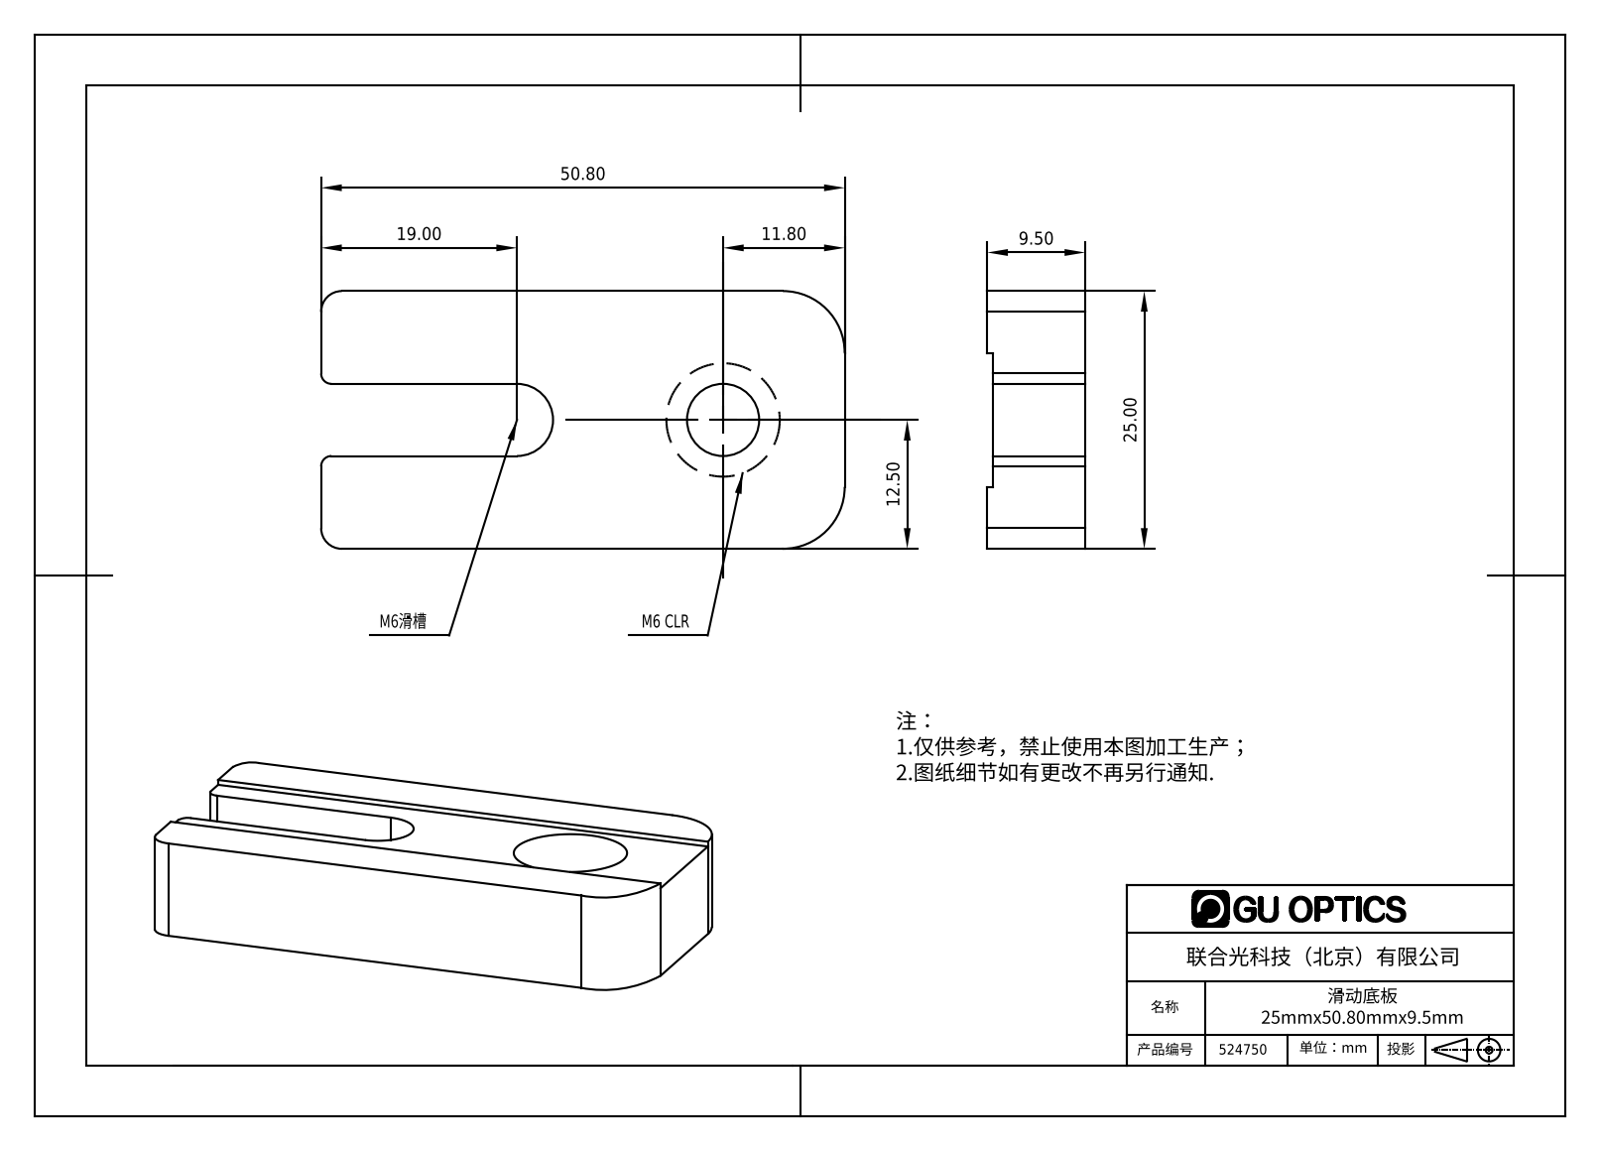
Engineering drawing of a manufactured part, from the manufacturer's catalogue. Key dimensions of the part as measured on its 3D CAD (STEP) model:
Part name (STEP PRODUCT): SB-05
STEP written by: SolidWorks 2012 (CONFIG_CONTROL_DESIGN)
Units: millimetres
Bodies: 1 solid, 23 faces (14 planar, 9 cylindrical, 0 other)
Overall size (bounding box): 50.8 × 25 × 9.5
Volume: 9 512 mm³ · Surface area: 4 180 mm²
Round holes (diameter × count): ⌀7 ×1, ⌀11 ×1
Partial cylindrical surfaces — rounded edges, fillets, slot ends (radius × count): R1 ×2, R2 ×2, R6 ×2, R3.5 ×1
Main face-to-face distances: 9, 9.5, 0.5, 25, 16, 7, 50.8, 3, 6, 6.5
